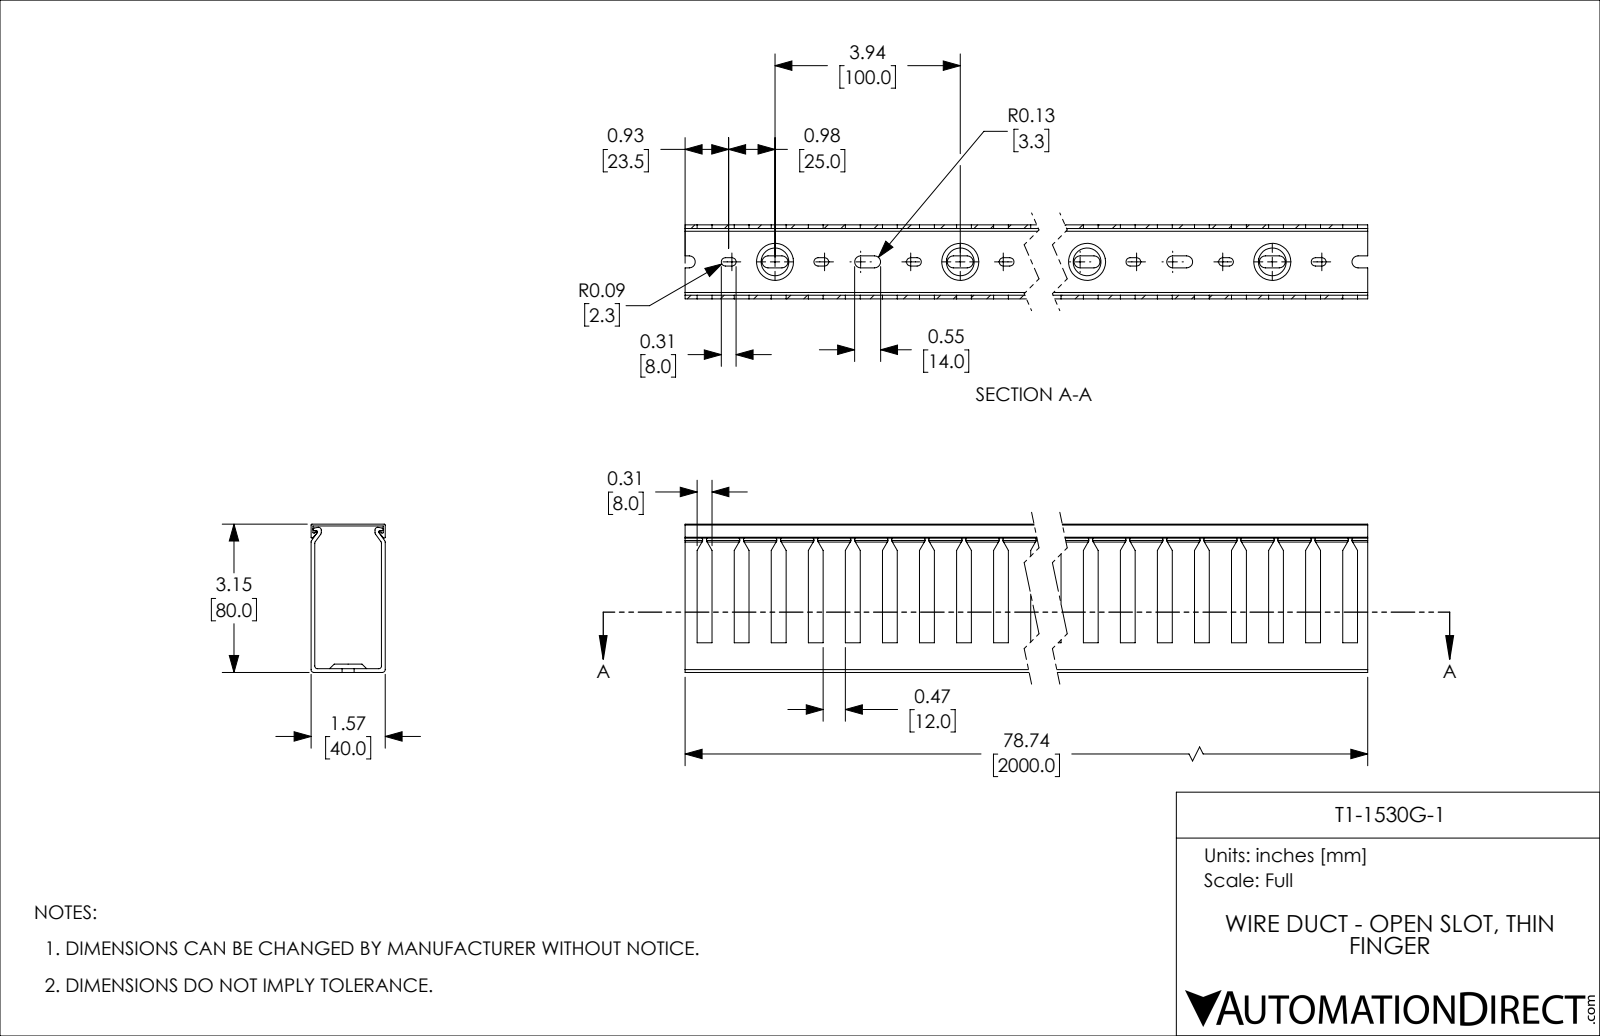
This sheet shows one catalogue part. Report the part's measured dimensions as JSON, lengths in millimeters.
{"part_name": "T1-1530K-1", "step_written_by": "SolidWorks 2021 (CONFIG_CONTROL_DESIGN)", "units": "millimeters", "bodies": {"solids": 2, "faces": 1005, "planar": 534, "cylindrical": 431, "other": 40}, "overall_size": [2000, 80, 40], "volume_mm3": 890552, "surface_area_mm2": 1009000, "partial_cylinders_radius": [[2.25, 80], [3.25, 80], [1.5, 12], [0.5, 8], [0.75, 6]], "face_to_face_distances": [2, 38, 40, 36, 1, 80, 79, 77, 78, 39]}
